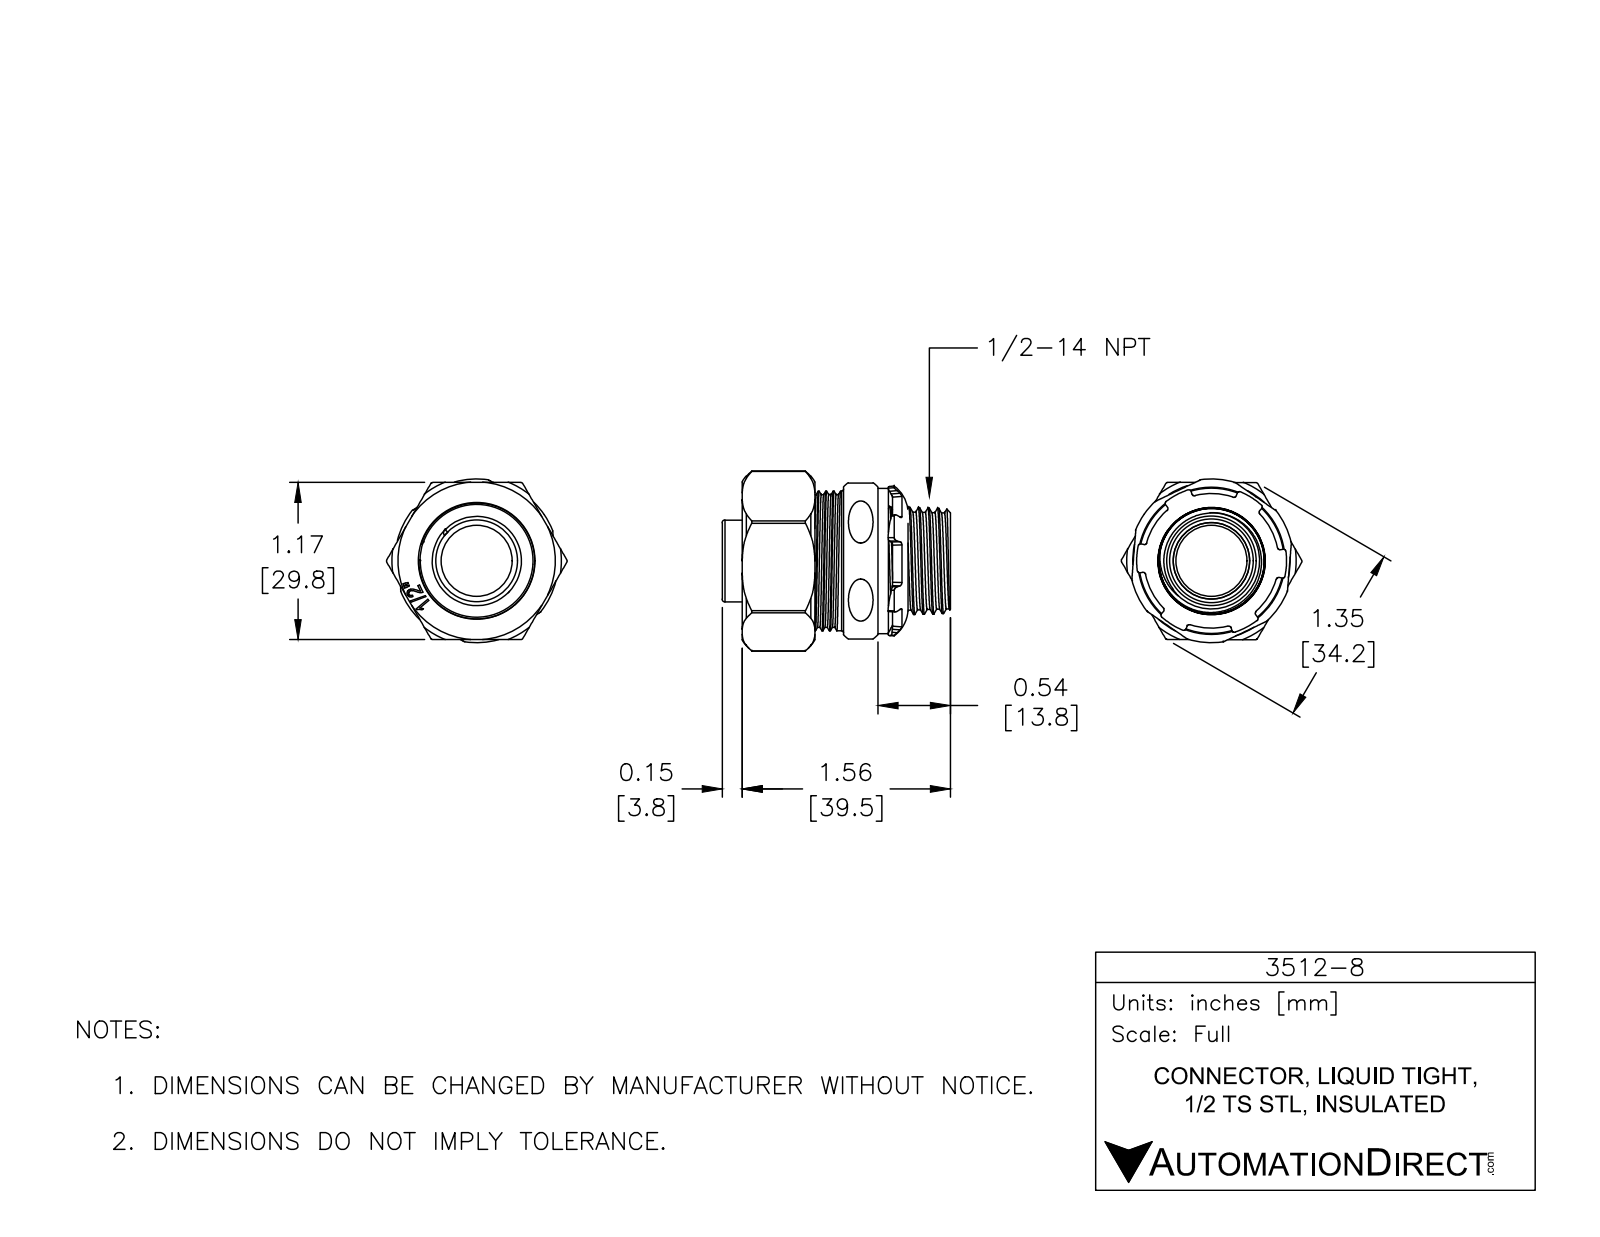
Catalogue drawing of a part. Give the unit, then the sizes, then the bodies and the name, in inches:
Units: inches
Overall size (bounding box): 1.762 × 1.344 × 1.22
Round holes (diameter × count): ⌀0.105 ×1, ⌀0.529 ×1, ⌀0.571 ×1, ⌀0.847 ×1, ⌀0.858 ×1, ⌀0.87 ×1, ⌀0.883 ×1, ⌀1.016 ×1
Round bosses / shafts (diameter × count): ⌀1.083 ×1, ⌀1.043 ×1, ⌀0.992 ×1, ⌀0.886 ×1, ⌀0.709 ×1, ⌀0.61 ×1, ⌀0.569 ×1, ⌀0.086 ×1
Partial cylindrical surfaces — rounded edges, fillets, slot ends (radius × count): R0.007 ×8, R0.02 ×6, R0.034 ×2, R0.009 ×1, R0.013 ×1, R0.025 ×1, R0.334 ×1
Main face-to-face distances: 1.013, 1.092, 0.079, 1.172, 1.174, 1.173, 0.933, 0.08, 0.159, 0.543
Hole centre spacings: 0.5
Volume: 0.652 in³ · Surface area: 26.89 in²
Bodies: 7 solids, 520 faces (197 planar, 98 cylindrical, 225 other)
Part name (STEP PRODUCT): 3512-8
STEP written by: SolidWorks 2018 (AUTOMOTIVE_DESIGN)
